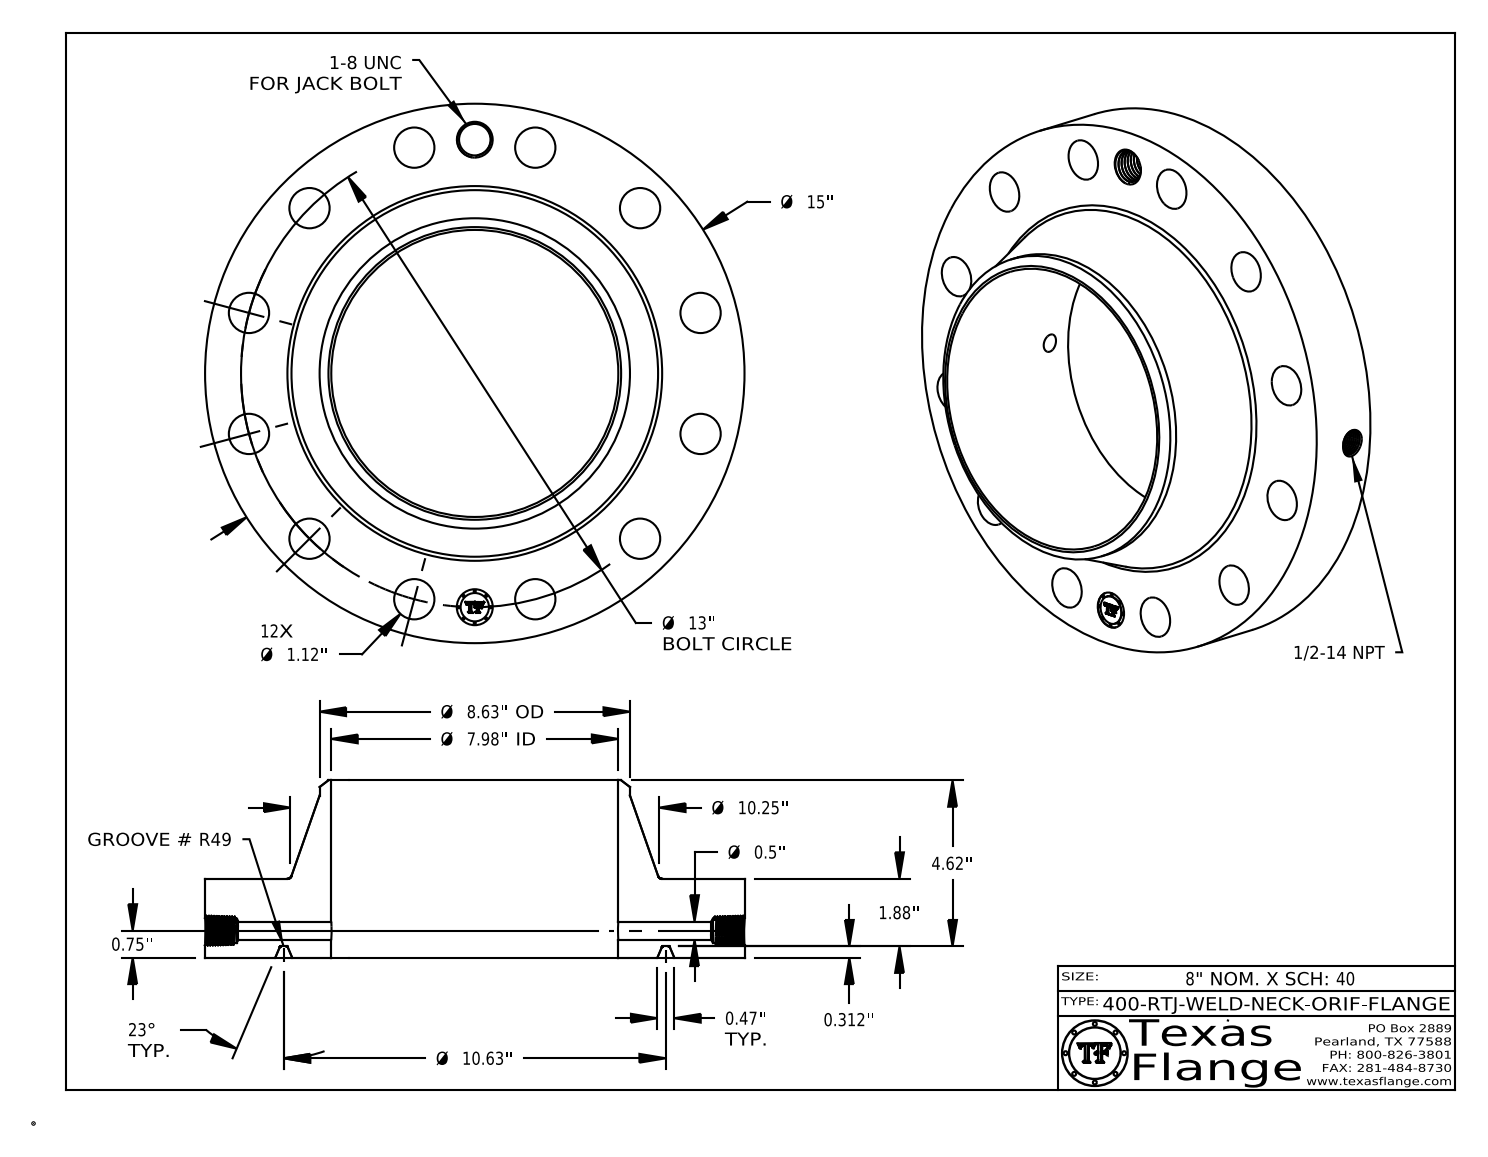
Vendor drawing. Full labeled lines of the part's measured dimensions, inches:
Part name (STEP PRODUCT): 400-RTJ-WELD-NECK
STEP written by: CATIA V5 STEP AP214 (AUTOMOTIVE_DESIGN)
Units: inches
Bodies: 1 solid, 801 faces (370 planar, 104 cylindrical, 327 other)
Overall size (bounding box): 15 × 15 × 4.932
Volume: 294.6 in³ · Surface area: 641.1 in²
Round holes (diameter × count): ⌀1.12 ×12, ⌀0.5 ×1, ⌀0.672 ×1, ⌀0.875 ×1, ⌀1 ×1, ⌀7.981 ×1
Round bosses / shafts (diameter × count): ⌀0.061 ×8, ⌀15 ×1, ⌀8.63 ×1, ⌀0.788 ×1
Main face-to-face distances: 2.192, 0.312, 1.88, 4.932, 4.62, 2.74, 2.177, 1.865, 0.015, 2.755
Hole centre spacings: 6.5, 3.365, 9.192, 11.258, 12.557, 13, 1.697, 4.975
